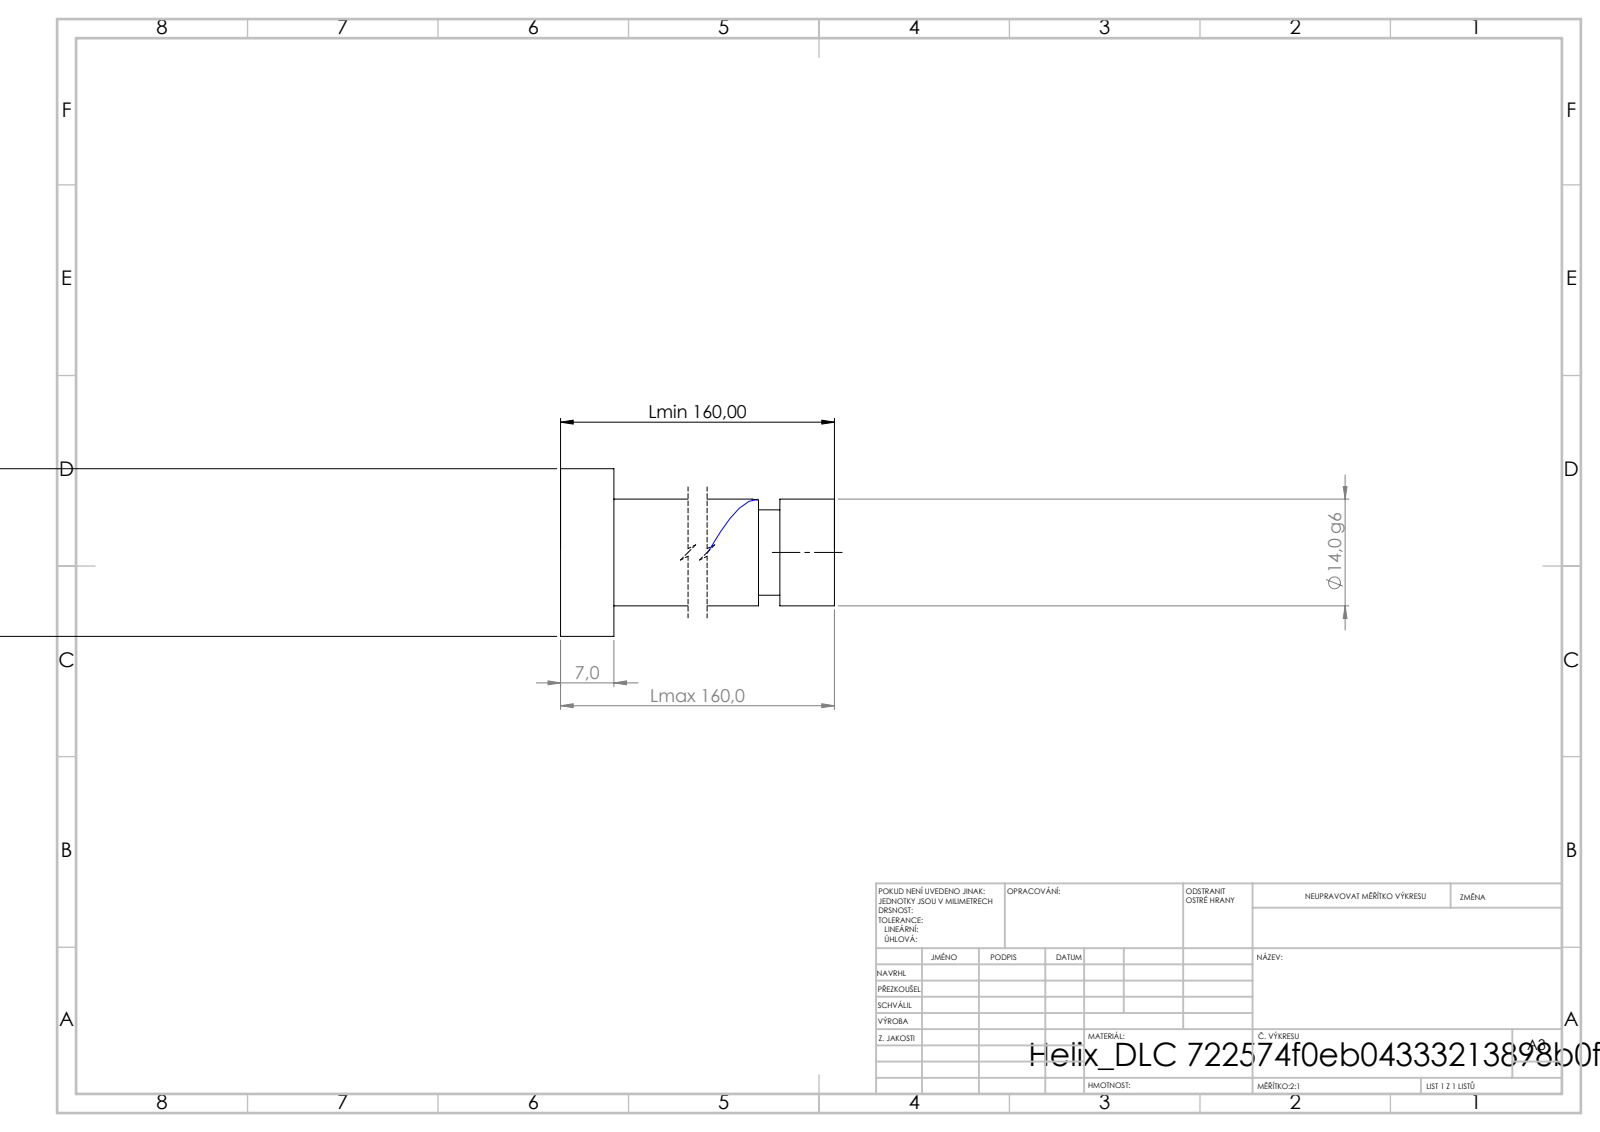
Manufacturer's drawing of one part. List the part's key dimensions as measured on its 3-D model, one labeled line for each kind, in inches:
STEP written by: SolidWorks 2019 (CONFIG_CONTROL_DESIGN)
Units: inches
Bodies: 1 solid, 21 faces (6 planar, 14 cylindrical, 1 other)
Overall size (bounding box): 6.299 × 0.866 × 0.866
Volume: 1.576 in³ · Surface area: 12.9 in²
Round bosses / shafts (diameter × count): ⌀0.866 ×1, ⌀0.551 ×1, ⌀0.441 ×1
Main face-to-face distances: 0.276, 6.299, 6.024, 6.017, 5.741, 0.282, 5.907, 5.631, 0.11, 0.393
